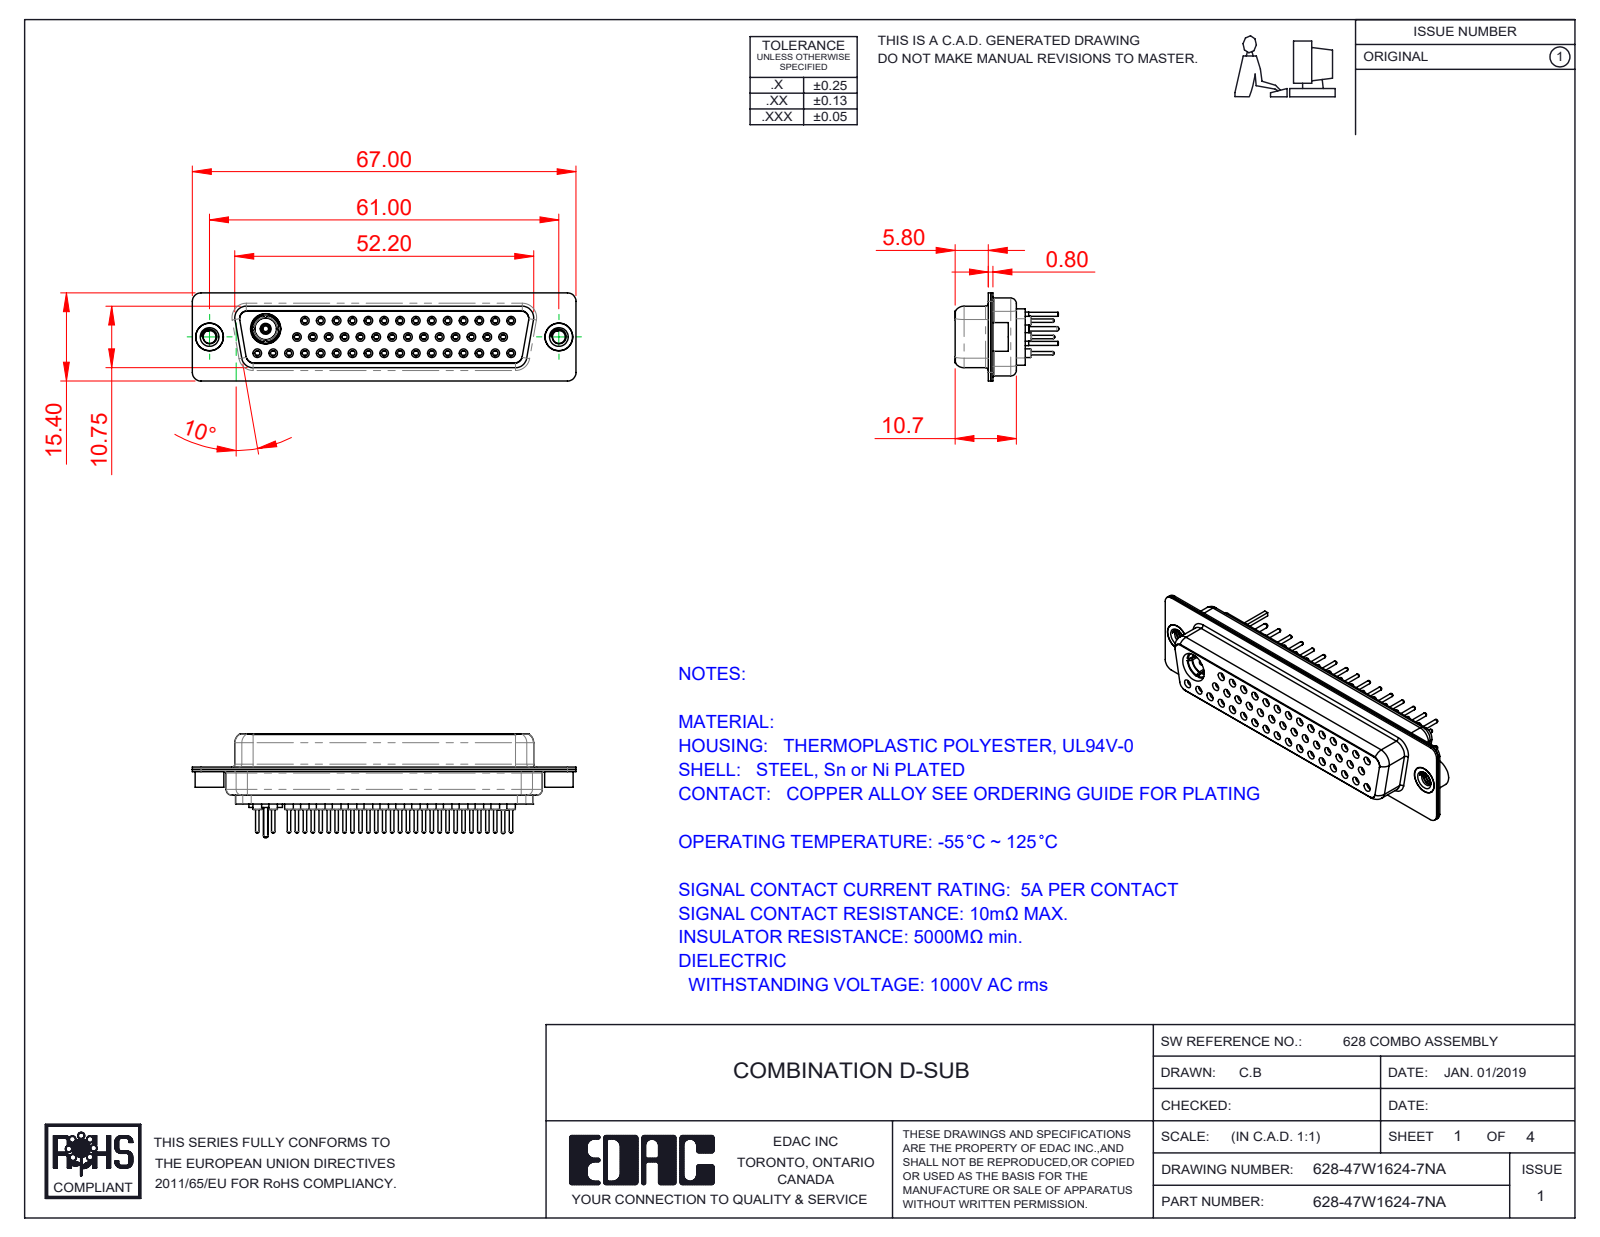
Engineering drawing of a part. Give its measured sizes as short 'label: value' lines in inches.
name: 628Combo Contact Row 1_24; Locking Collar; 628Combo Housing_47W1; 628Combo Threaded Rivet_A (+8 more)
written by: SolidWorks 2016 (CONFIG_CONTROL_DESIGN)
unit: in
bodies: 55 solids, 2921 faces (811 planar, 1050 cylindrical, 1060 other)
size: 2.638 × 0.715 × 0.606
volume: 0.43 in³; area: 23.06 in²
holes: 47× ⌀0.043, 46× ⌀0.059, 45× ⌀0.035, 45× ⌀0.079, 31× ⌀0.063, 14× ⌀0.067, 3× ⌀0.191, 2× ⌀0.089, 2× ⌀0.157, 2× ⌀0.159, 1× ⌀0.111, 1× ⌀0.13
bosses: 46× ⌀0.087, 46× ⌀0.024, 15× ⌀0.063, 3× ⌀0.197, 2× ⌀0.195, 2× ⌀0.189, 1× ⌀0.23, 1× ⌀0.205
rounds: 16× R0.059, 12× R0.053, 12× R0.079, 8× R0.063, 4× R0.01, 4× R0.02, 4× R0.024, 4× R0.026
face distances: 0.016, 0.238, 0.254, 0.446, 0.074, 0.482, 0.244, 0.228, 0.407, 0.43
hole spacings: 0.124, 0.109, 0.218, 0.327, 0.436, 0.545, 0.654, 0.763
